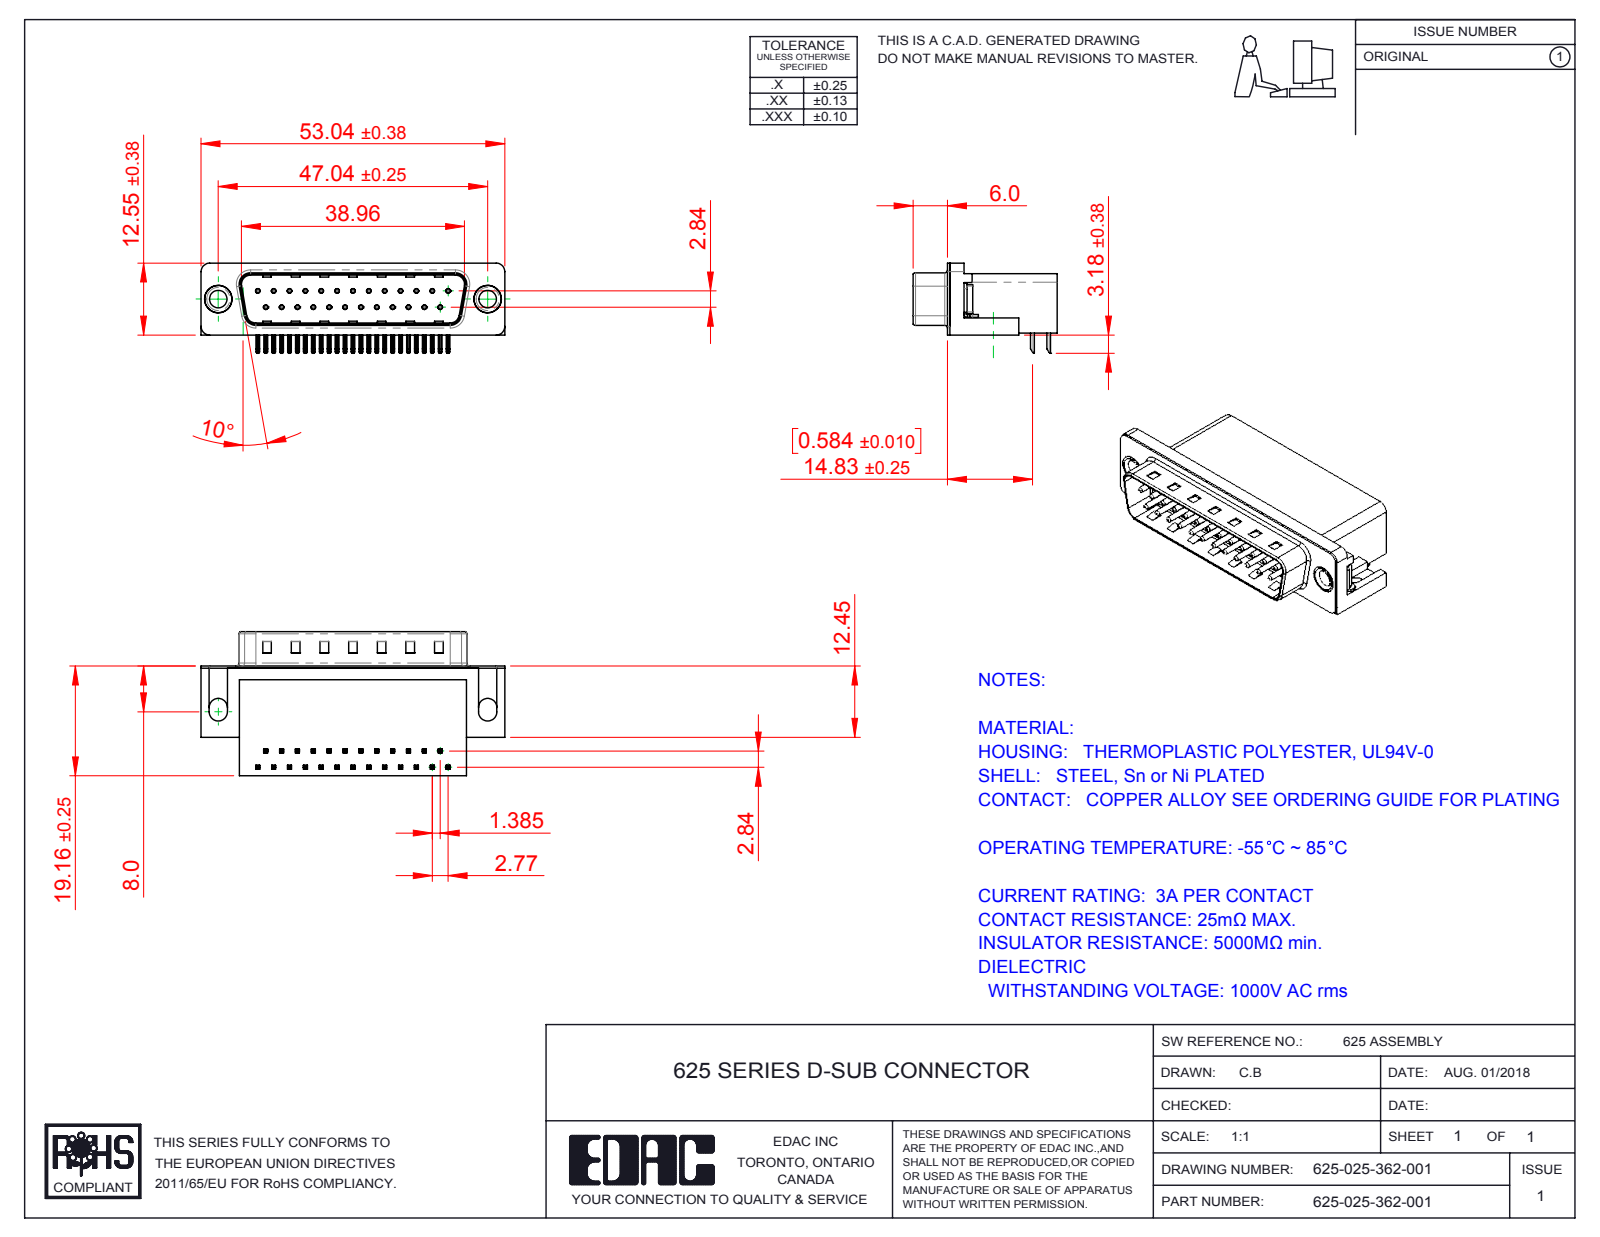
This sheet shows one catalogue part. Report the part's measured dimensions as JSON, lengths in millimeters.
{"part_name": "625 Housing_25 Socket; 625 Non Board Mount; 625 Contact Top; 625 Thru Hole Rivet (+3 more)", "step_written_by": "SolidWorks 2016 (CONFIG_CONTROL_DESIGN)", "units": "millimeters", "bodies": {"solids": 31, "faces": 2223, "planar": 1407, "cylindrical": 639, "other": 177}, "overall_size": [53.04, 25.16, 15.73], "volume_mm3": 9125, "surface_area_mm2": 8704, "round_holes": [[0.35, 25], [0.8, 25], [3.05, 2], [4, 2], [4.8, 2], [5, 2]], "round_bosses_or_shafts": [[0.75, 25], [4.9, 2], [4.75, 2], [3.85, 2]], "partial_cylinders_radius": [[0.25, 108], [0.12, 50], [1, 16], [0.5, 9], [1.6, 8], [1.5, 7], [0.9, 4], [2, 4]], "face_to_face_distances": [0.4, 10.35, 18.76, 2.1, 8.76, 10.46, 10.86, 1.7, 19.16, 10.11], "hole_center_spacings": [3.16, 2.77, 11.08, 5.54, 8.31, 5.03, 13.85, 7.48]}
